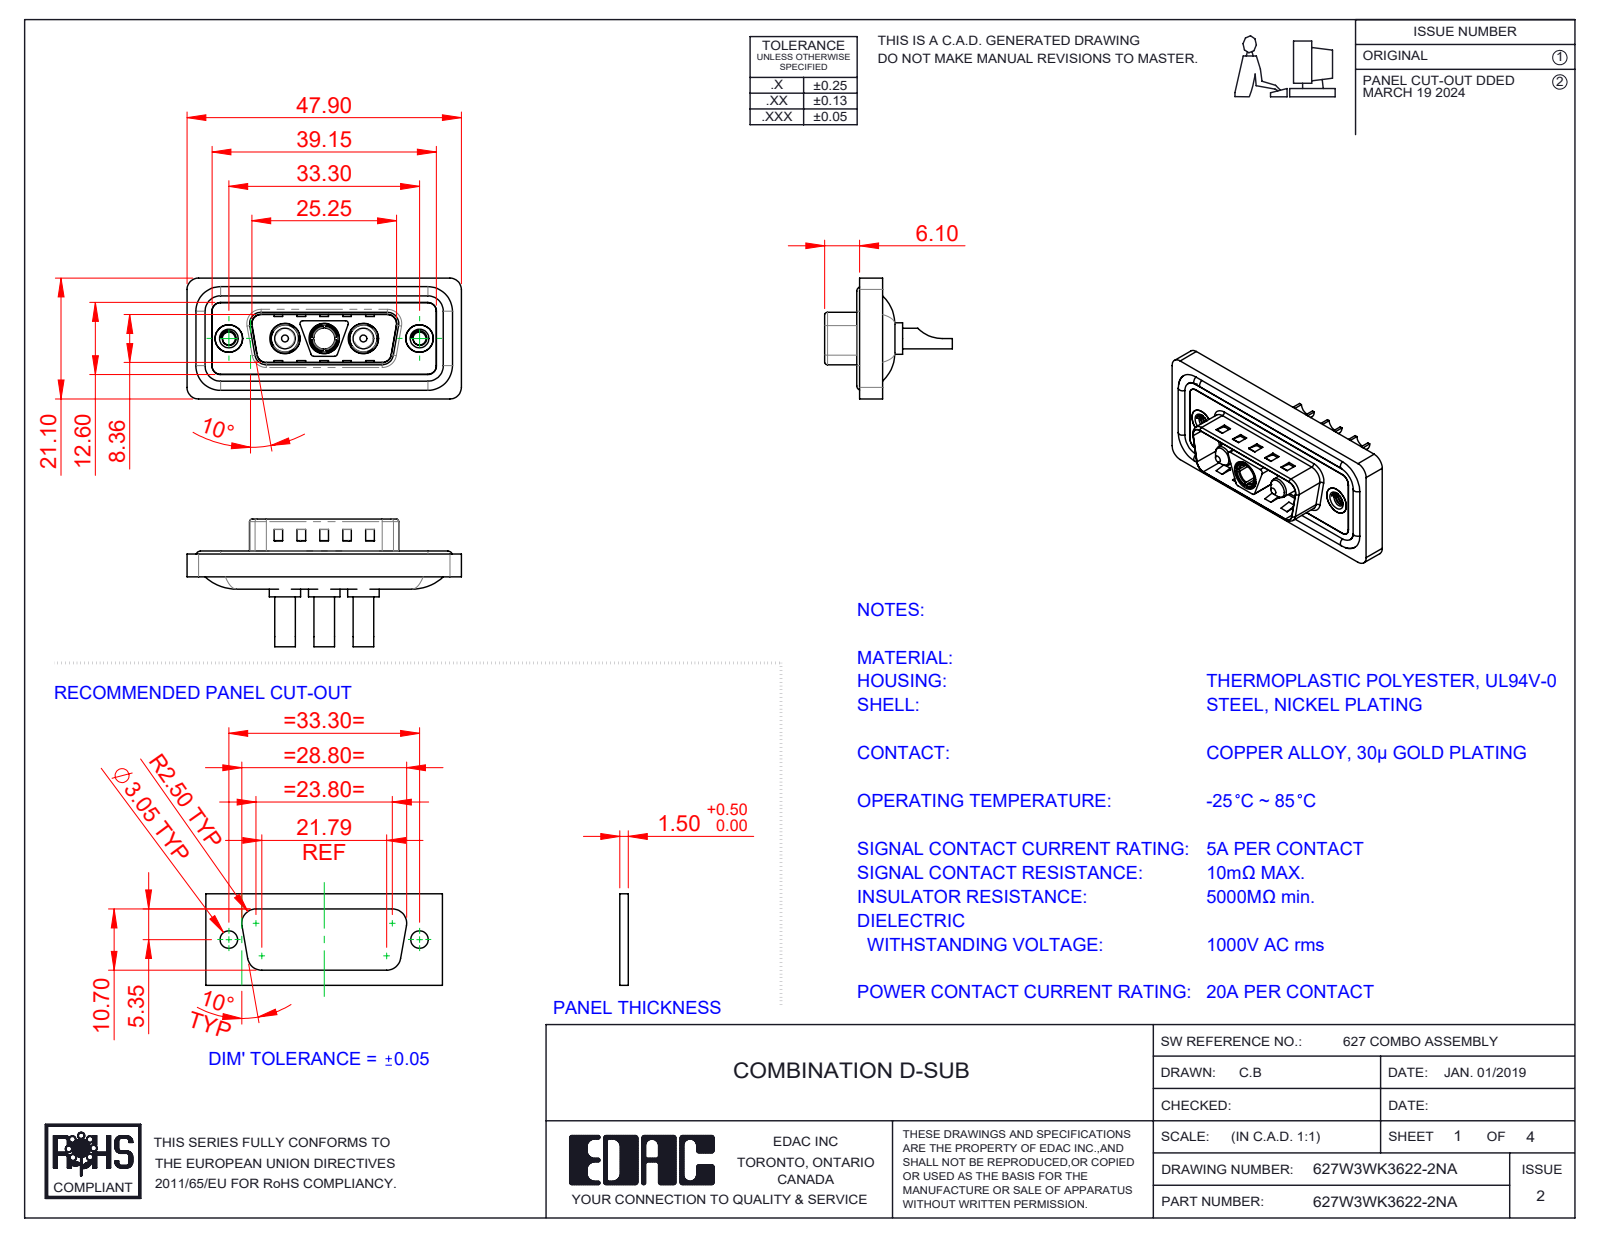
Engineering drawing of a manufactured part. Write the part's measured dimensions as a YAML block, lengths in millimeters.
part_name: "627Combo Threaded Rivet_A; Power Pin_20A SC; 627W3WK3622-2NA; 627Combo Shell Front_15 Contacts (+4 more)"
step_written_by: "SolidWorks 2023 (CONFIG_CONTROL_DESIGN)"
units: millimeters
bodies: {solids: 13, faces: 628, planar: 240, cylindrical: 261, other: 127}
overall_size: [47.9, 22.3, 21.1]
volume: 5728
surface_area: 9372
round_holes:
  - {diameter: 2.7, count: 3}
  - {diameter: 4.85, count: 3}
  - {diameter: 5.3, count: 3}
  - {diameter: 2.26, count: 2}
  - {diameter: 4, count: 2}
  - {diameter: 4.8, count: 2}
  - {diameter: 5, count: 2}
  - {diameter: 3.7, count: 1}
round_bosses_or_shafts:
  - {diameter: 1.6, count: 4}
  - {diameter: 5.5, count: 3}
  - {diameter: 5.2, count: 3}
  - {diameter: 4.75, count: 3}
  - {diameter: 3.75, count: 3}
  - {diameter: 3.6, count: 3}
  - {diameter: 4.9, count: 2}
  - {diameter: 4.96, count: 1}
partial_cylinders:
  - {radius: 1.5, count: 26}
  - {radius: 2, count: 20}
  - {radius: 0.5, count: 12}
  - {radius: 1.6, count: 8}
  - {radius: 0.25, count: 4}
  - {radius: 0.6, count: 4}
  - {radius: 0.65, count: 4}
  - {radius: 0.9, count: 4}
face_to_face_distances: [0.4, 1.1, 0.5, 1.5, 1.6, 3.1, 2.9, 4, 0.82, 9.58]
hole_center_spacings: [6.85, 9.8, 16.65, 23.5, 13.7, 33.3]
